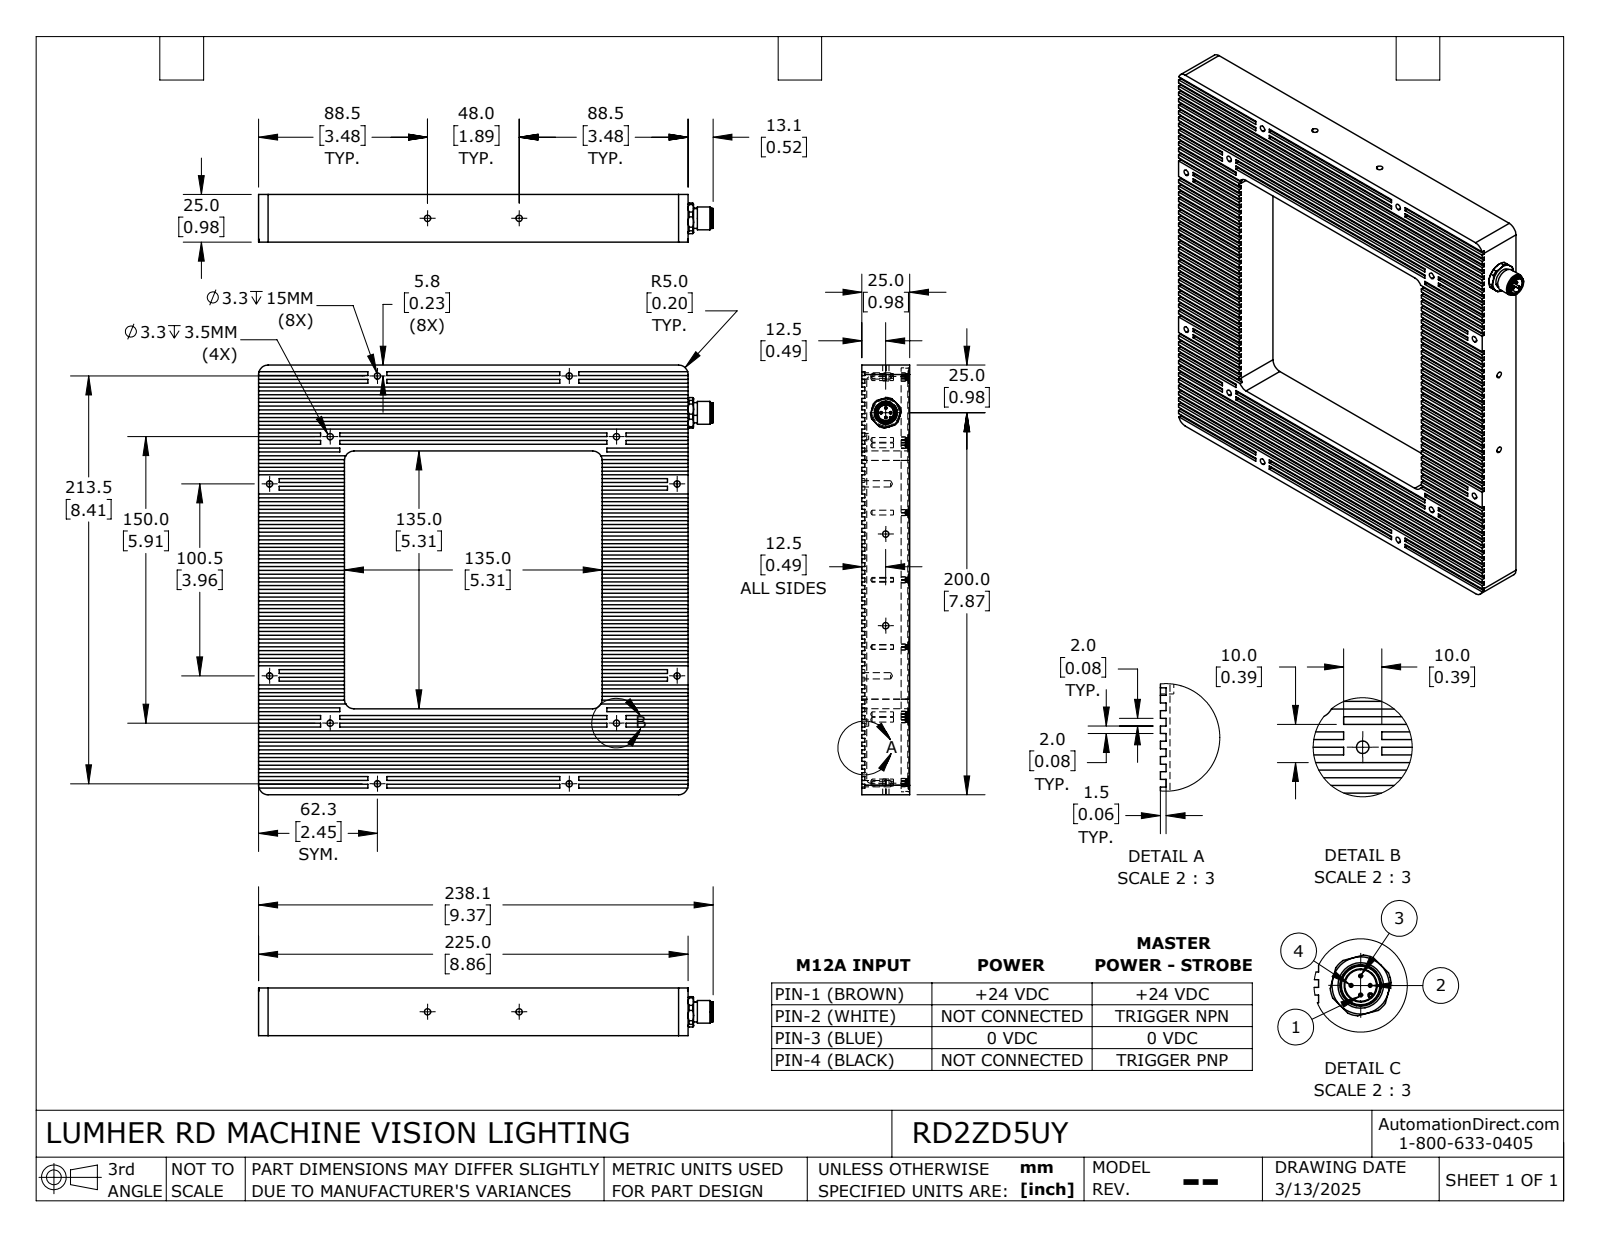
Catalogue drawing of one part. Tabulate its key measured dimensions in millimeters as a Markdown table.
| quantity | value |
| --- | --- |
| part name | RD2ZD5UY |
| STEP written by | SolidWorks 2024 (AUTOMOTIVE_DESIGN) |
| units | millimeters |
| bodies | 1 solid, 3276 faces (670 planar, 1729 cylindrical, 877 other) |
| overall size | 238.1 × 225 × 25 |
| volume | 766 576 mm³ |
| surface area | 145 055 mm² |
| round holes (diameter × count) | 3.2 × 40, 2.5 × 38, 3.3 × 16, 1.45 × 4, 8.3 × 1, 9.4 × 1, 11 × 1, 12.2 × 1 |
| round bosses / shafts (diameter × count) | 5.6 × 40, 3 × 40, 0.8 × 40, 1.4 × 4, 1 × 4, 11.91 × 1, 11.9 × 1, 10.6 × 1 |
| partial cylindrical surfaces (radius × count) | 0.57 × 480, 0.25 × 240, 1.02 × 40, 5 × 8, 2 × 4, 3.3 × 4, 3.5 × 4, 6.5 × 4 |
| main face-to-face distances | 1.5, 24.5, 180, 23, 45, 43.5, 135, 225, 43.3, 1.7 |
| hole center spacings | 40.26, 129.21, 166.86, 183.43, 220.73, 55.34, 155.83, 183.15 |
